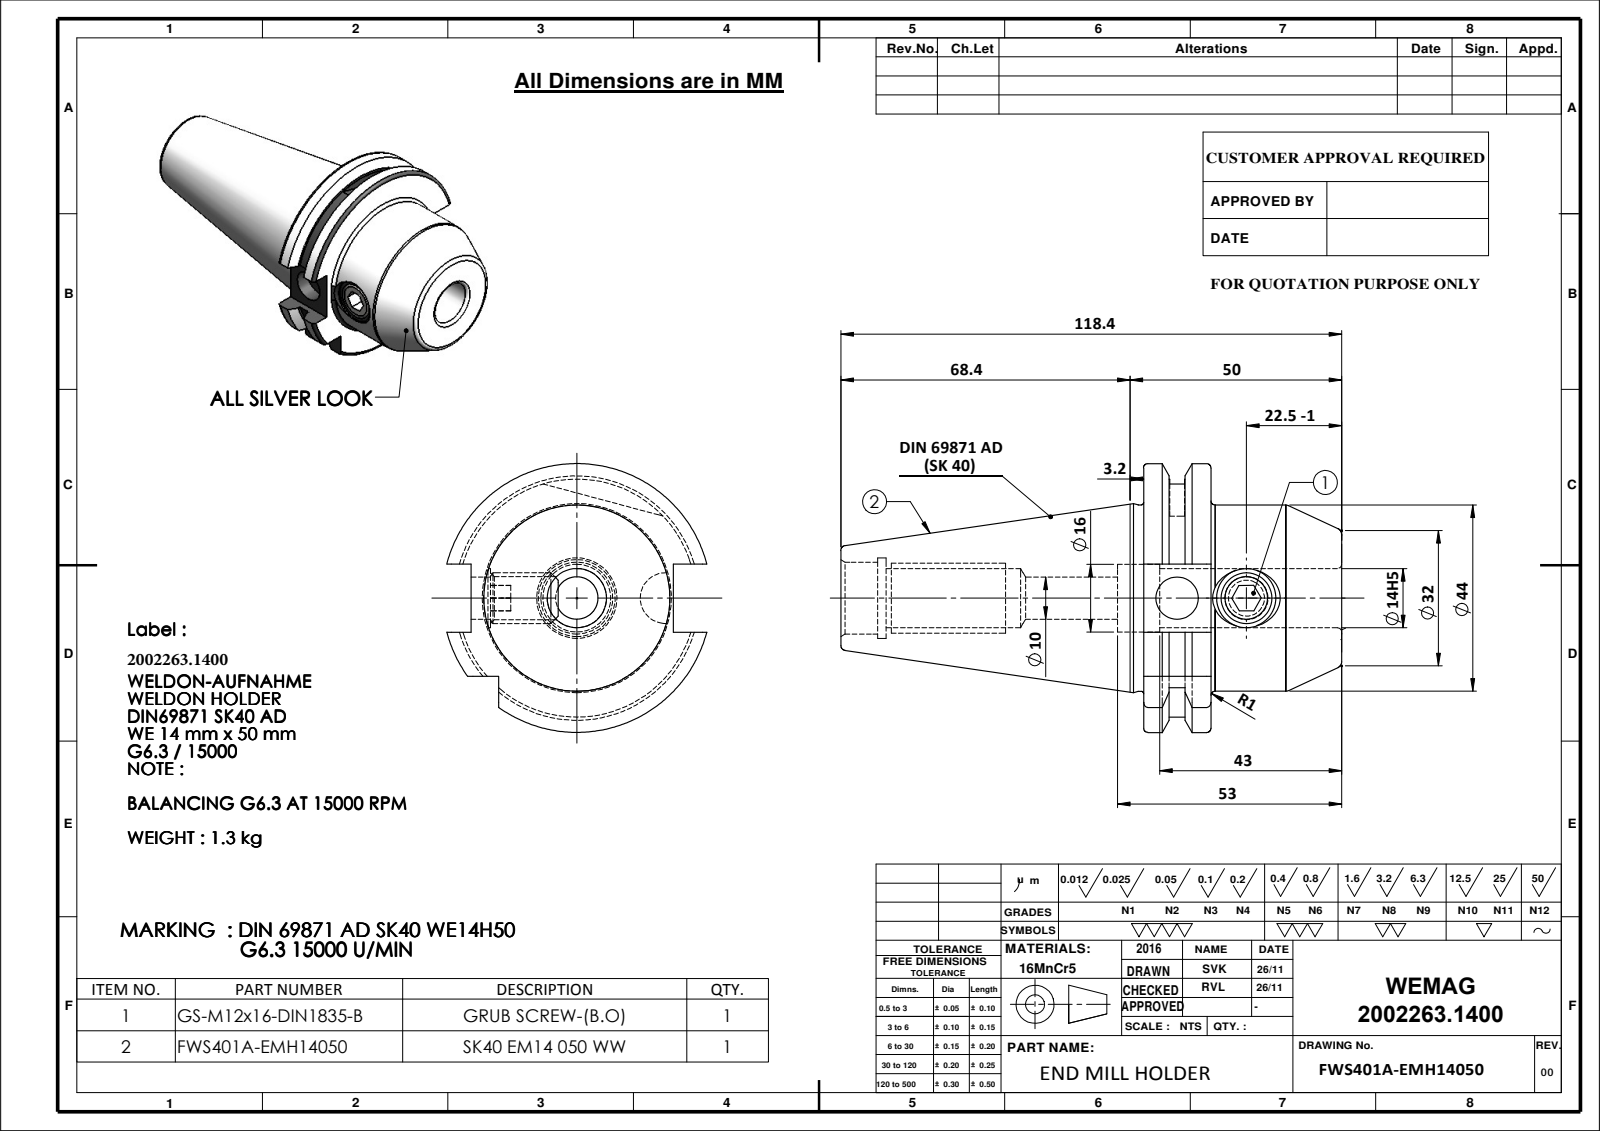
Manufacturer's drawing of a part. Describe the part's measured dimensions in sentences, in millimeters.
The part is named "SK40 EM 14 050 WW; M12X16_ISO 4026 - M12 x 12-N; 91406-WE114050". Its 3-D file was written by "SolidWorks 2009 (CONFIG_CONTROL_DESIGN)". It is 2 solids with 125 faces: 36 planar, 36 cylindrical and 53 other. Overall it measures 118.4 by 63.55 by 61.48 millimeters. Its volume is 137 092 cubic millimeters and its surface area 26 754 square millimeters. Round holes: 2 of diameter 10, 2 of diameter 14, 1 of diameter 10.2, 1 of diameter 16, 1 of diameter 17, 1 of diameter 19. Round bosses or shafts: 1 of diameter 44.05, 1 of diameter 44, 1 of diameter 12. Partial cylindrical surfaces (rounded edges, fillets, slot ends): 1 of radius 28.12, 1 of radius 31.77. The main face-to-face distances are 15.9, 46.8, 30.9, 16.1, 47.8, 4.6, 43.2, 71.6, 87.5, 118.4. The hole center spacings are 16.4.
